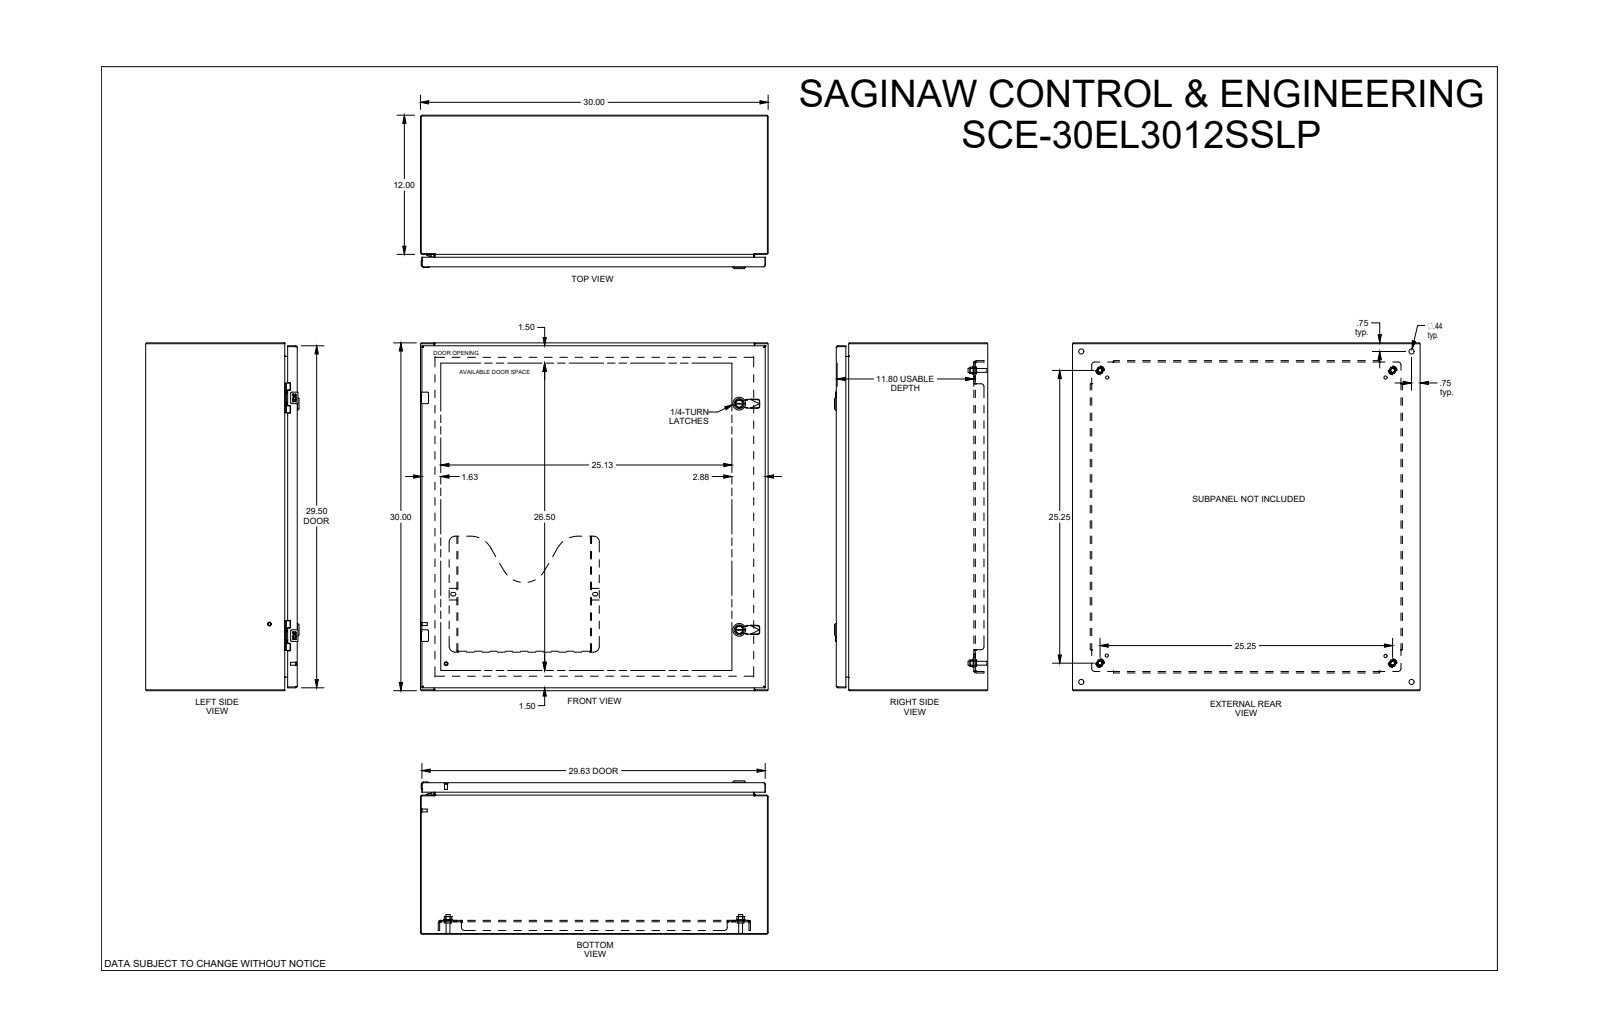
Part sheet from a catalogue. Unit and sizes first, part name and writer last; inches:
Units: inches
Overall size (bounding box): 30 × 30 × 13.23
Round holes (diameter × count): ⌀0.172 ×4, ⌀0.205 ×4, ⌀0.244 ×4, ⌀0.266 ×4, ⌀0.281 ×4, ⌀0.367 ×4, ⌀0.437 ×4, ⌀0.5 ×4, ⌀0.375 ×3, ⌀0.156 ×2, ⌀0.197 ×2, ⌀0.218 ×2
Round bosses / shafts (diameter × count): ⌀0.17 ×6, ⌀0.366 ×4, ⌀0.332 ×4, ⌀0.25 ×4, ⌀0.248 ×4, ⌀0.196 ×3, ⌀1.102 ×2, ⌀0.866 ×2
Partial cylindrical surfaces — rounded edges, fillets, slot ends (radius × count): R0.012 ×56, R0.01 ×28, R0.015 ×28, R0.04 ×23, R0.02 ×20, R0.07 ×14, R0.029 ×12, R0.145 ×10
Main face-to-face distances: 0.075, 29.925, 0.075, 12.923, 12.998, 13.073, 12.998, 1.2, 11.873, 0.125
Hole centre spacings: 0.985, 26.352, 26.924, 20.5, 24.639, 0.02, 0.875, 4.493
Bodies: 0 solids, 2838 faces (1307 planar, 759 cylindrical, 772 other)
Part name (STEP PRODUCT): SCE-30EL3012SSLP
STEP written by: SolidWorks 2019 (CONFIG_CONTROL_DESIGN)
